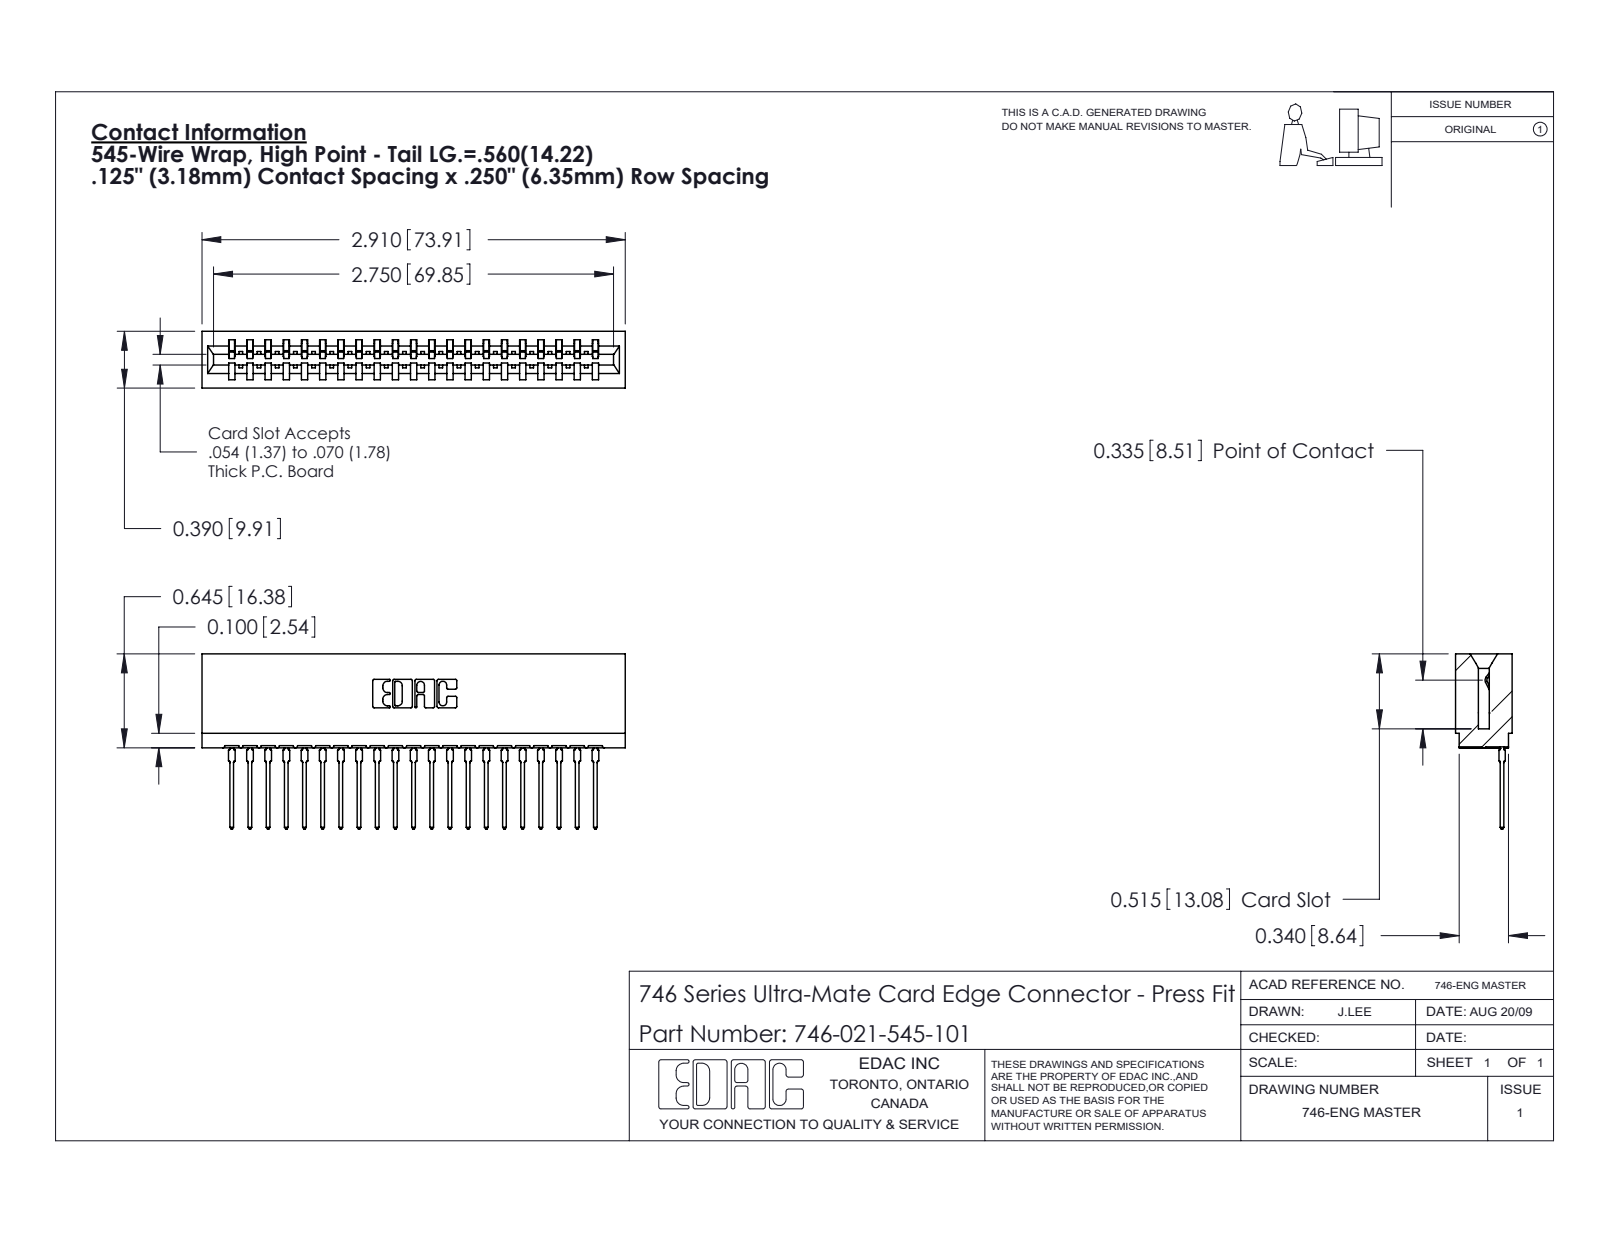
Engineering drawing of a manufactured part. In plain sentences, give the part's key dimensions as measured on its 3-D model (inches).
The part is named "746-292-001_545; 746-021-545-101; 746 Part_.515 Slot Depth - 01". Its 3-D file was written by "SolidWorks 2020 (CONFIG_CONTROL_DESIGN)". It is 22 solids with 2365 faces: 1378 planar, 441 cylindrical and 546 other. Overall it measures 2.91 by 1.204 by 0.39 inches. Its volume is 0.483 cubic inches and its surface area 18.12 square inches. Partial cylindrical surfaces (rounded edges, fillets, slot ends): 42 of radius 0.021, 22 of radius 0.01, 22 of radius 0.015, 6 of radius 0.007, 6 of radius 0.031, 4 of radius 0.005, 4 of radius 0.011, 3 of radius 0.026. The main face-to-face distances are 0.25, 0.333, 0.057, 0.39, 0.5, 0.025, 0.307, 0.042, 0.125, 0.083.
